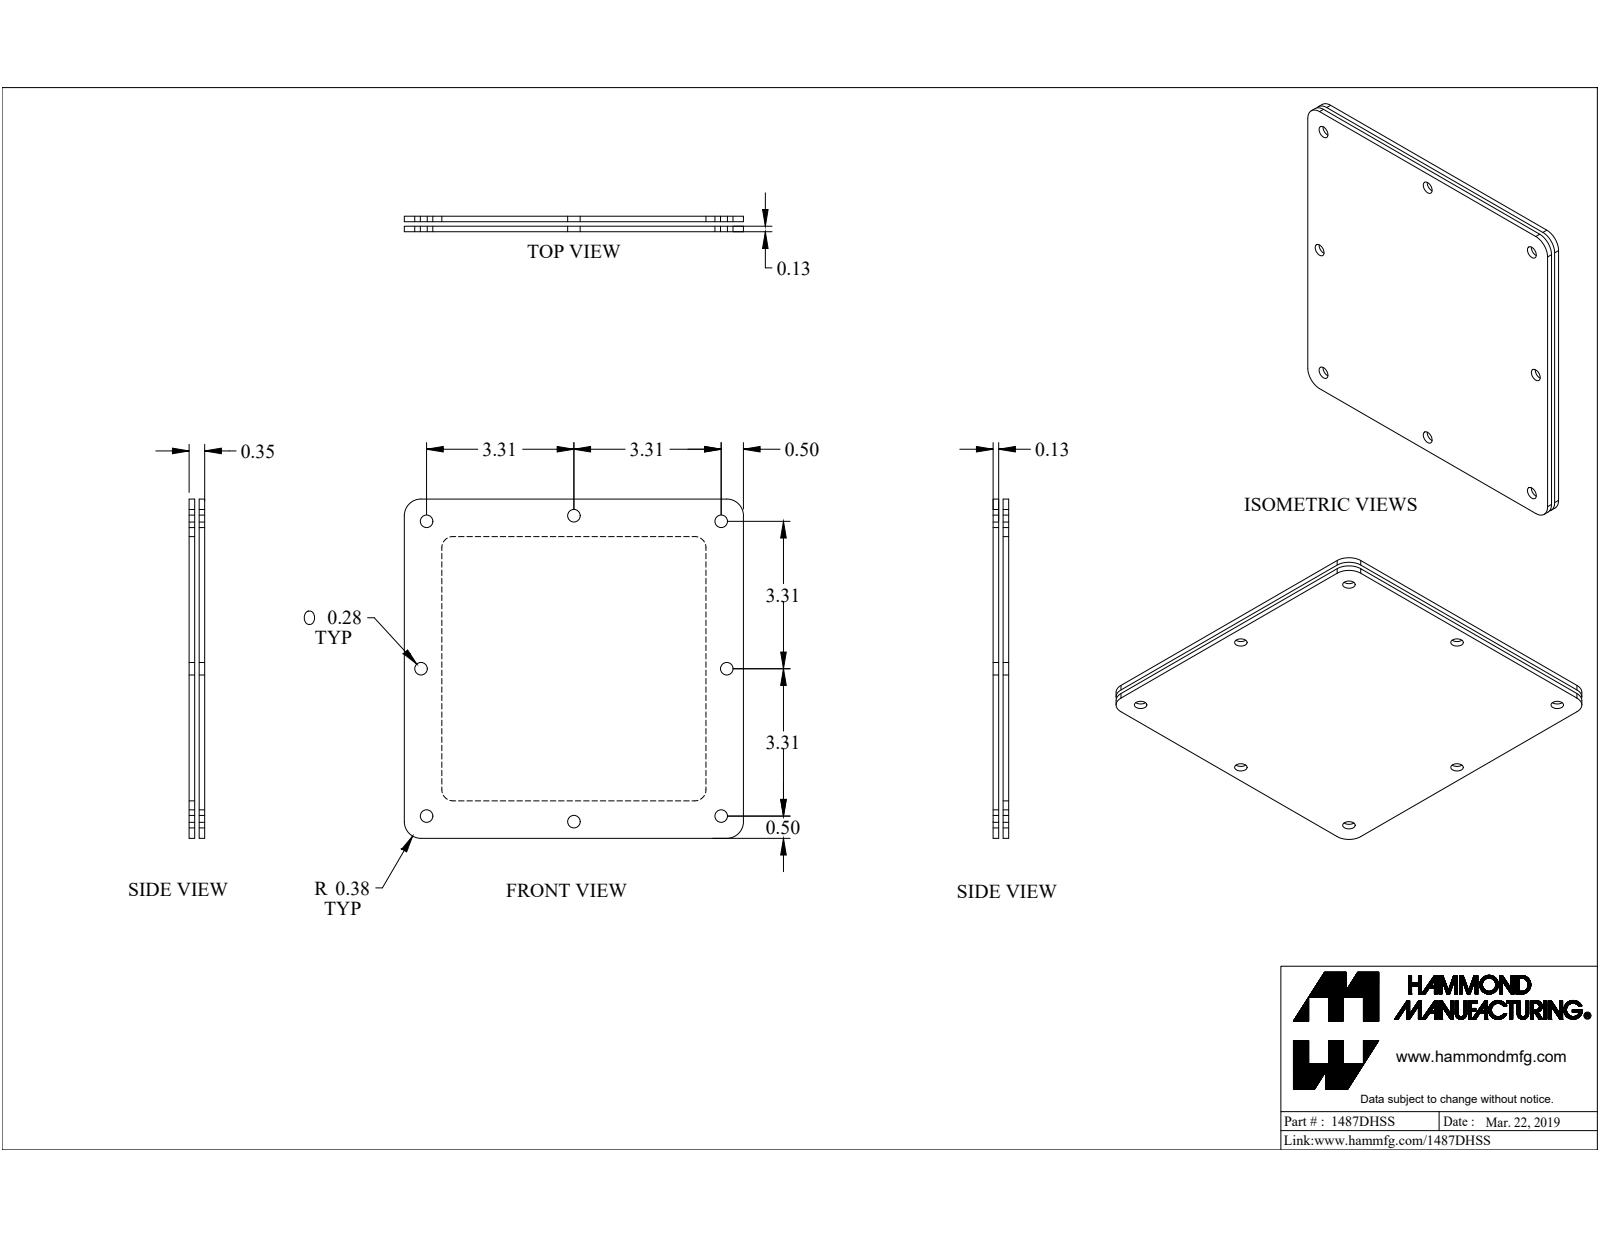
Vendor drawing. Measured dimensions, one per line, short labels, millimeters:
name: 1487DHSS
written by: SolidWorks 2019 (CONFIG_CONTROL_DESIGN)
unit: mm
bodies: 5 solids, 131 faces (73 planar, 50 cylindrical, 8 other)
size: 193.7 × 193.7 × 24.7
volume: 165 000 mm³; area: 112 300 mm²
holes: 8× ⌀7.1, 1× ⌀5, 1× ⌀6.6, 1× ⌀8.9
bosses: 1× ⌀12.7, 1× ⌀6.4
rounds: 6× R0.5, 4× R6.4, 4× R9.5
face distances: 3.2, 5.7, 8.9, 2.5, 193.7, 21.4, 172.3, 150.9, 6.4, 12.7
hole spacings: 84.2, 191, 123.5, 168.3, 174.6, 238
